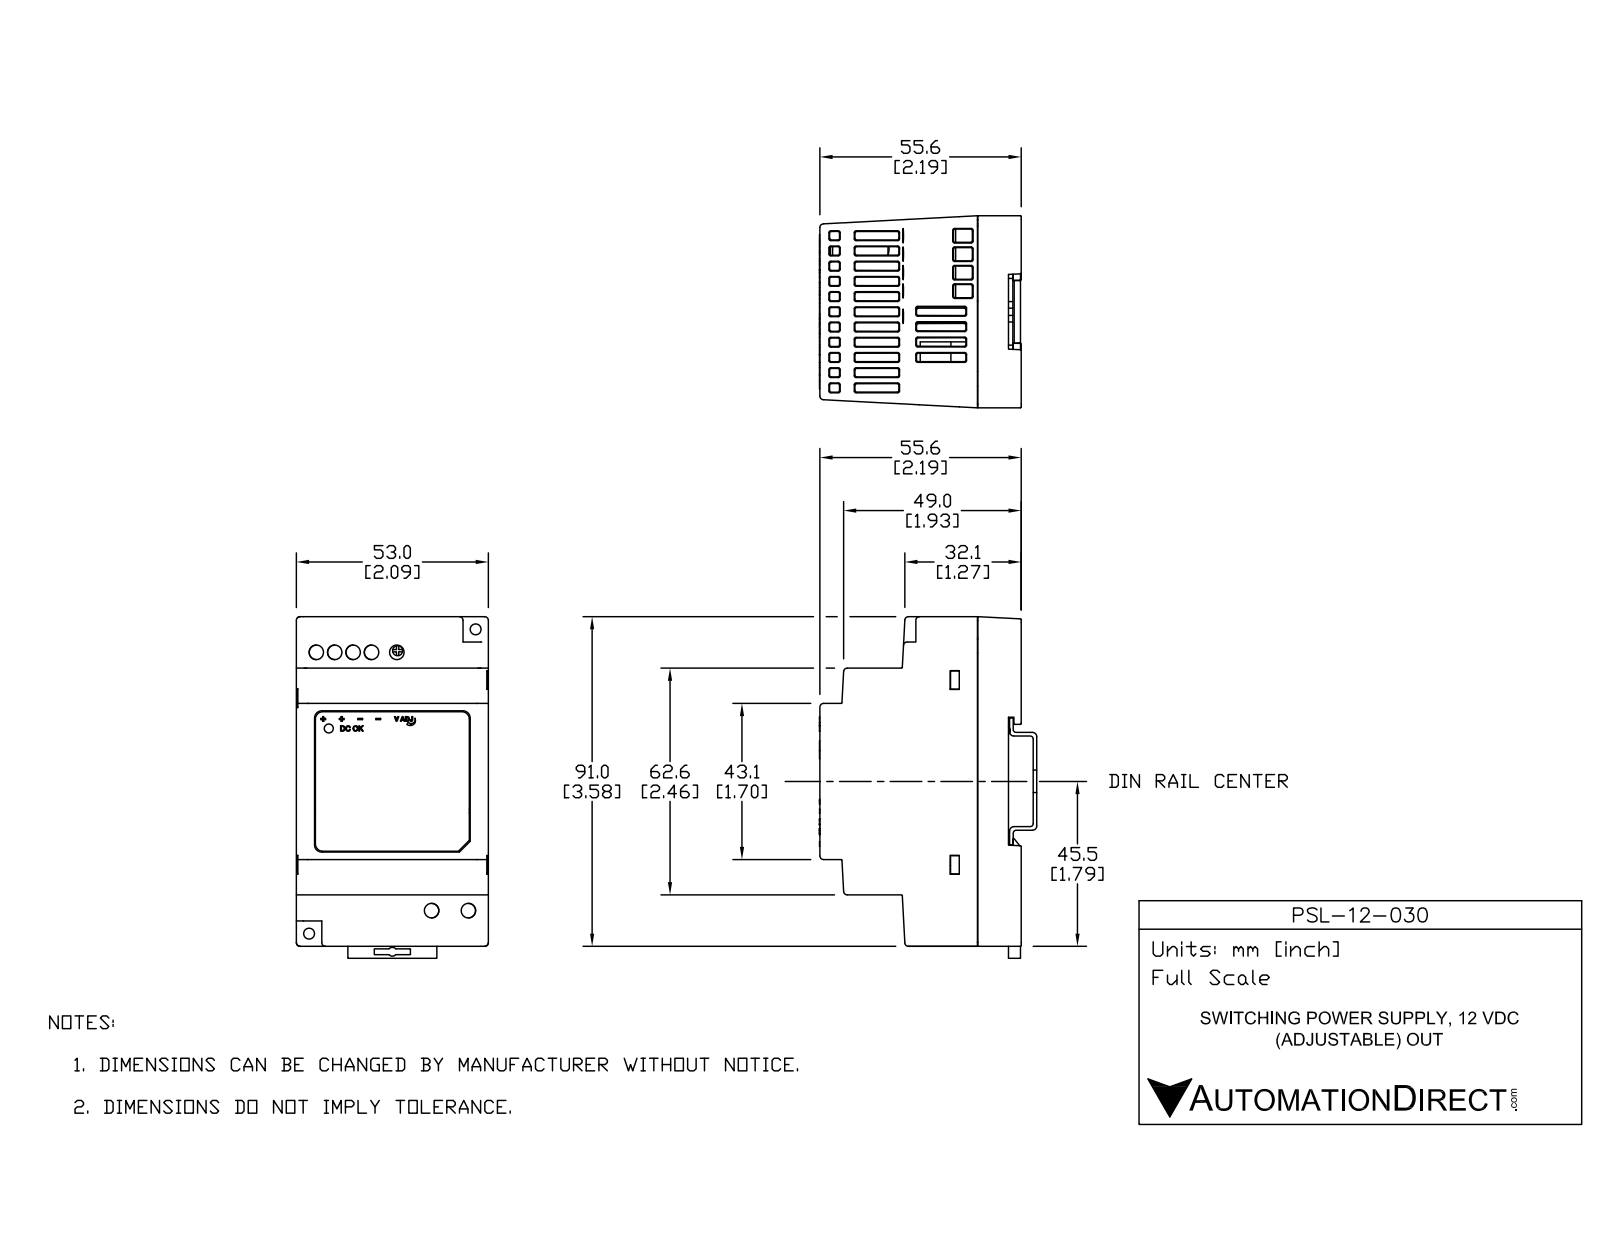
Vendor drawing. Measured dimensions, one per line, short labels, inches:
name: PSL-12-030
written by: SolidWorks 2017 (AUTOMOTIVE_DESIGN)
unit: in
bodies: 9 solids, 1253 faces (694 planar, 458 cylindrical, 101 other)
size: 3.713 × 2.189 × 2.087
volume: 3.283 in³; area: 96.09 in²
holes: 14× ⌀0.157, 2× ⌀0.098, 2× ⌀0.118, 2× ⌀0.138, 2× ⌀0.197, 1× ⌀0.109, 1× ⌀0.146, 1× ⌀0.159
bosses: 3× ⌀0.018, 1× ⌀0.197, 1× ⌀0.156
rounds: 236× R0.02, 85× R0.008, 58× R0.039, 3× R0.079, 2× R0.04, 2× R0.059, 2× R0.128, 1× R0.048
face distances: 0.079, 0.126, 0.173, 0.252, 0.047, 0.205, 1.972, 0.071, 1.791, 1.894
hole spacings: 0.2, 0.4, 2.998, 3.074, 2.967, 3.058, 3.094, 0.199
